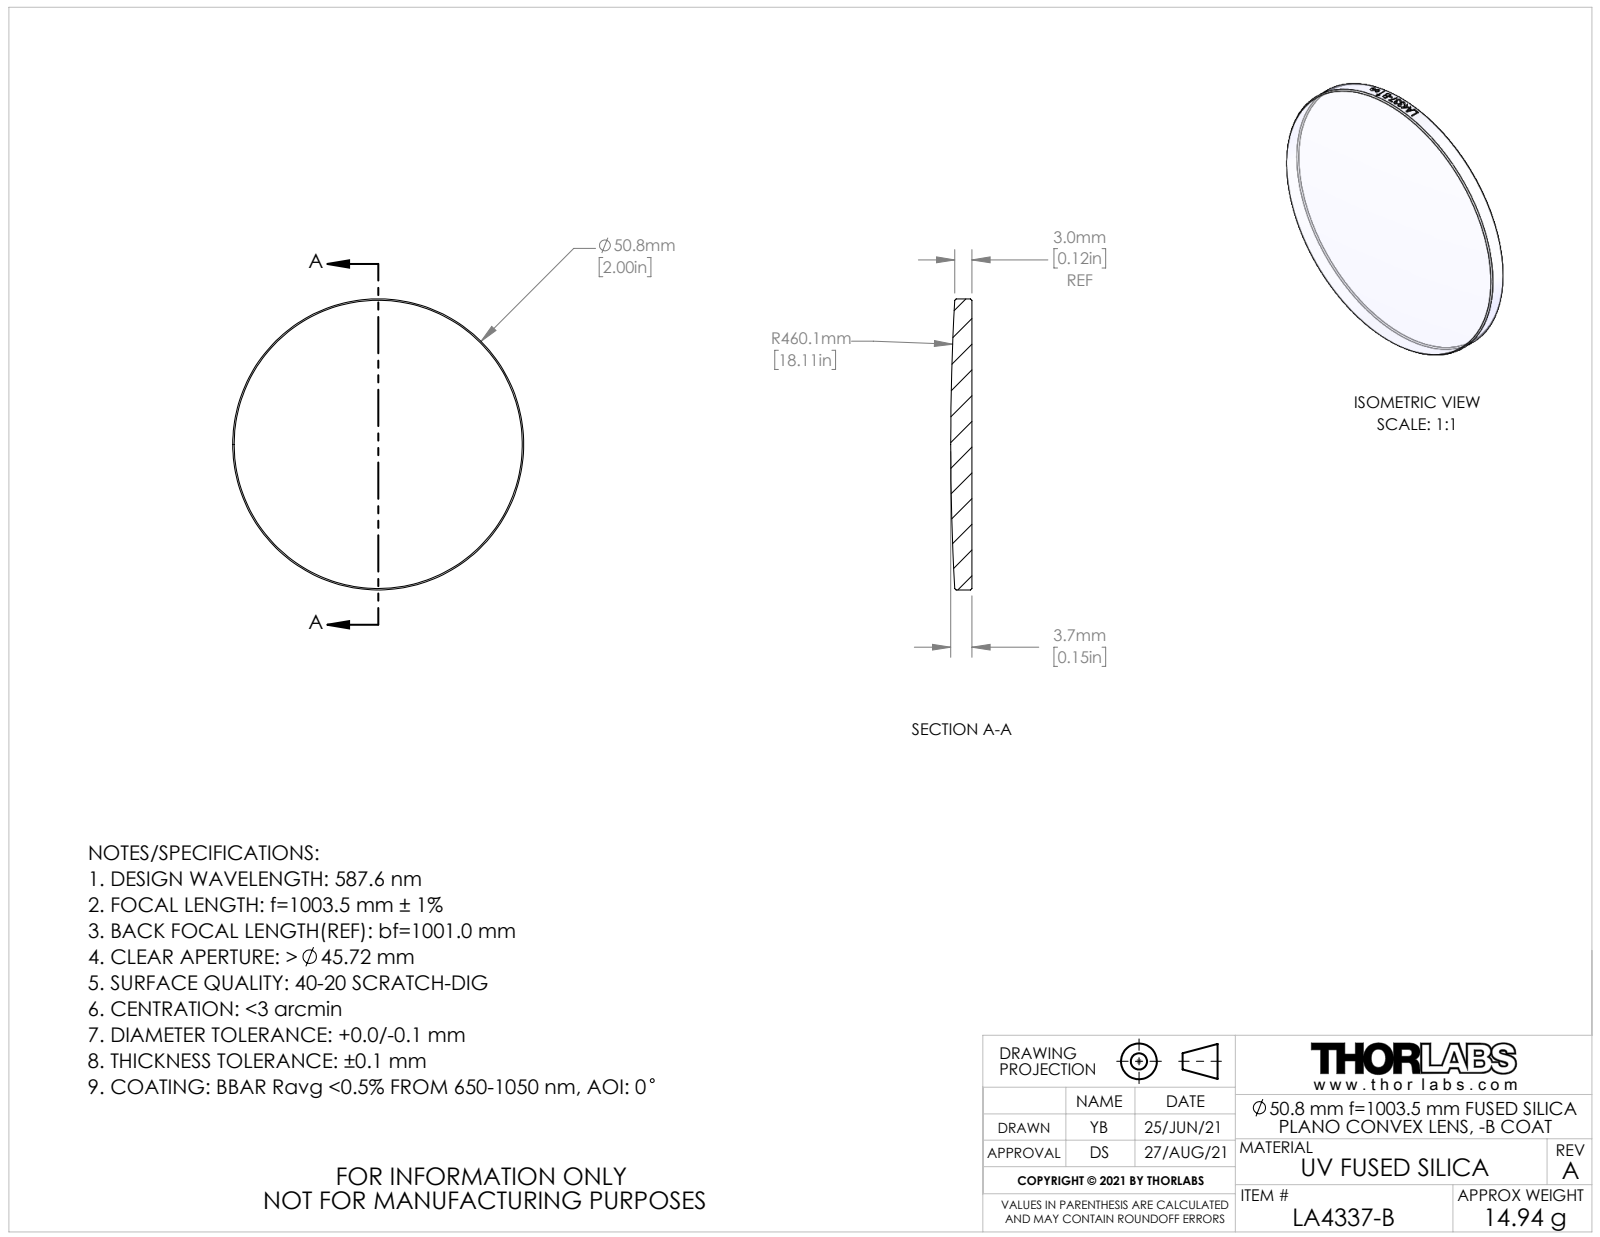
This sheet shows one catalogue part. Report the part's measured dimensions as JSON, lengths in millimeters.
{"part_name": "CTN017912-E0W", "step_written_by": "SolidWorks 2018 (AUTOMOTIVE_DESIGN)", "units": "millimeters", "bodies": {"solids": 1, "faces": 25, "planar": 1, "cylindrical": 18, "other": 6}, "overall_size": [50.8, 50.8, 3.7], "volume_mm3": 6781, "surface_area_mm2": 4489, "round_bosses_or_shafts": [[50.8, 1]]}
